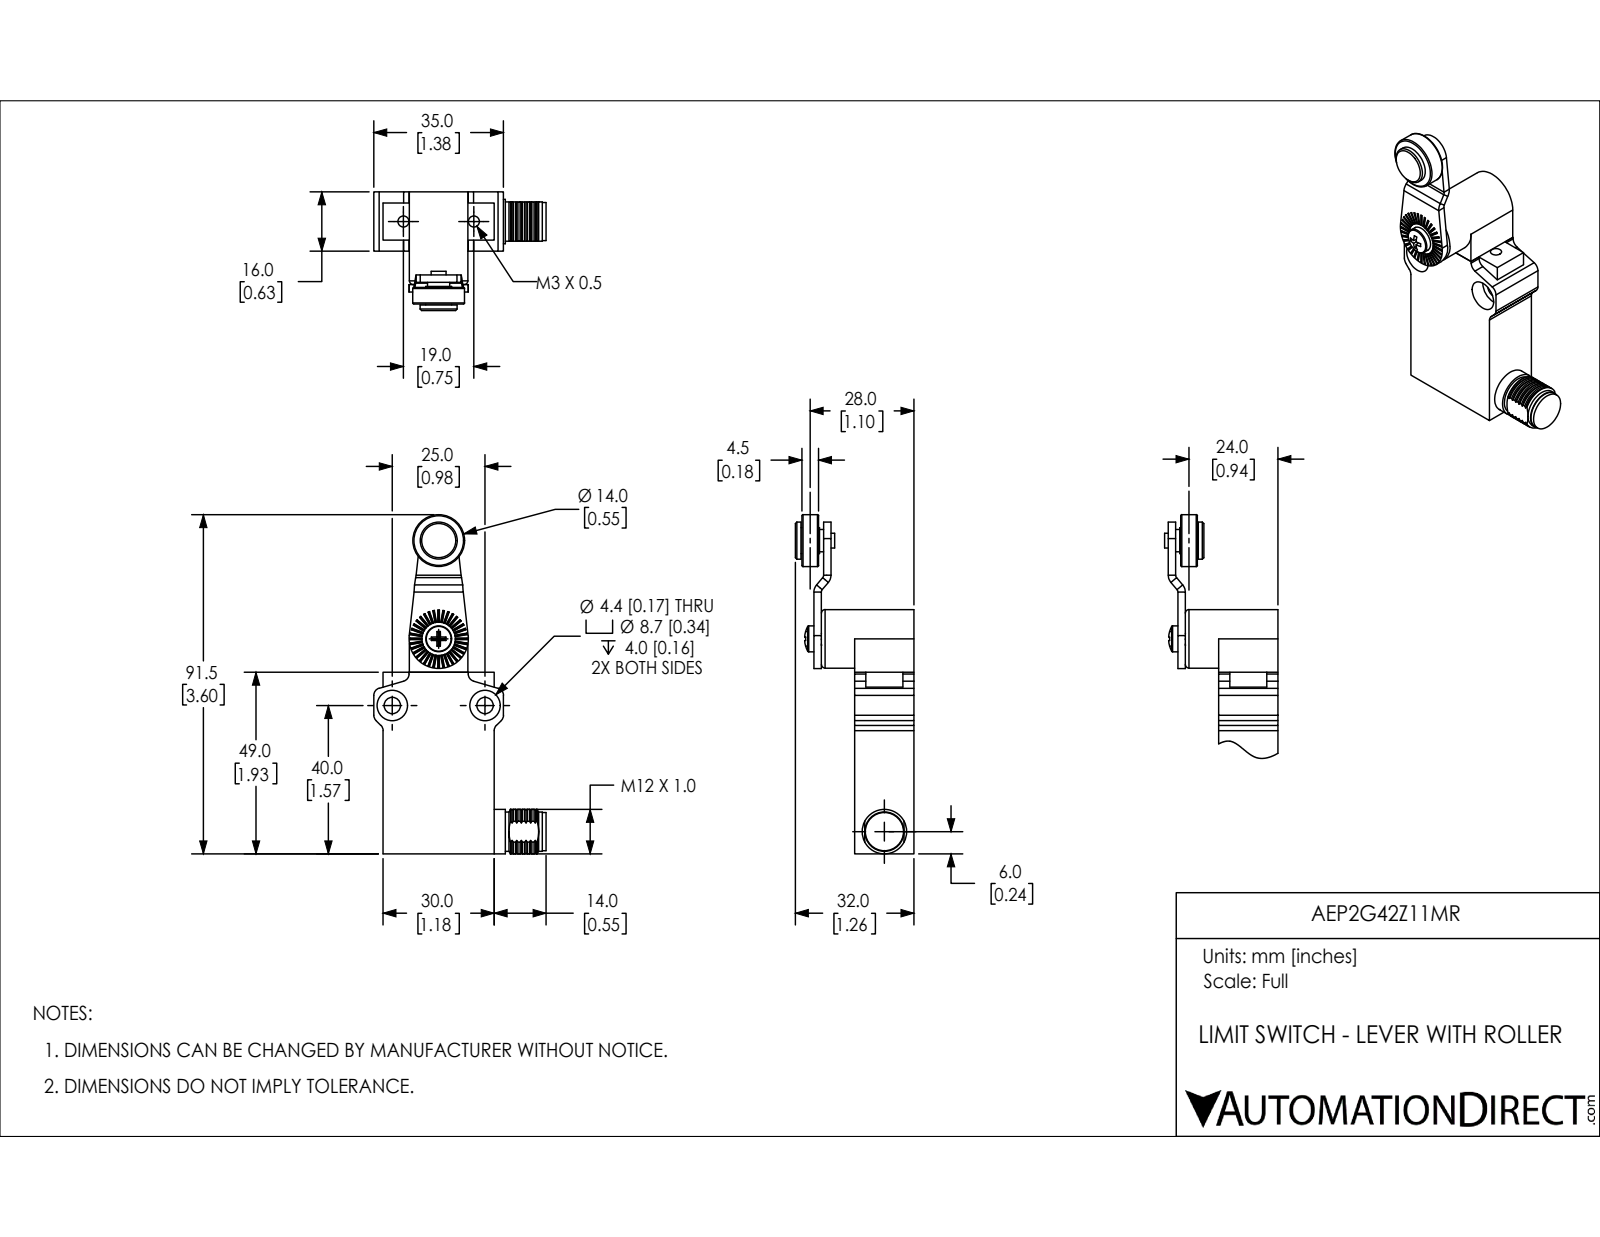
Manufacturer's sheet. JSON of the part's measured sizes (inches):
{"part_name": "AEP2G42Z11MR", "step_written_by": "SolidWorks 2018 (AUTOMOTIVE_DESIGN)", "units": "inches", "bodies": {"solids": 7, "faces": 657, "planar": 299, "cylindrical": 146, "other": 212}, "overall_size": [3.602, 1.831, 1.26], "volume_in3": 1.899, "surface_area_in2": 18.2, "round_holes": [[0.118, 2], [0.173, 2], [0.197, 2], [0.323, 2], [0.098, 1], [0.161, 1], [0.224, 1]], "round_bosses_or_shafts": [[0.276, 2], [0.622, 1], [0.551, 1], [0.472, 1], [0.417, 1], [0.406, 1], [0.394, 1], [0.236, 1]], "partial_cylinders_radius": [[0.079, 8], [0.039, 2], [0.118, 2], [0.256, 1], [0.315, 1]], "face_to_face_distances": [0.63, 1.181, 1.929, 0.354, 0.079, 0.984, 0.28, 0.902, 0.102, 0.472], "hole_center_spacings": [0.863, 1.82, 0.748, 0.984, 1.043]}
